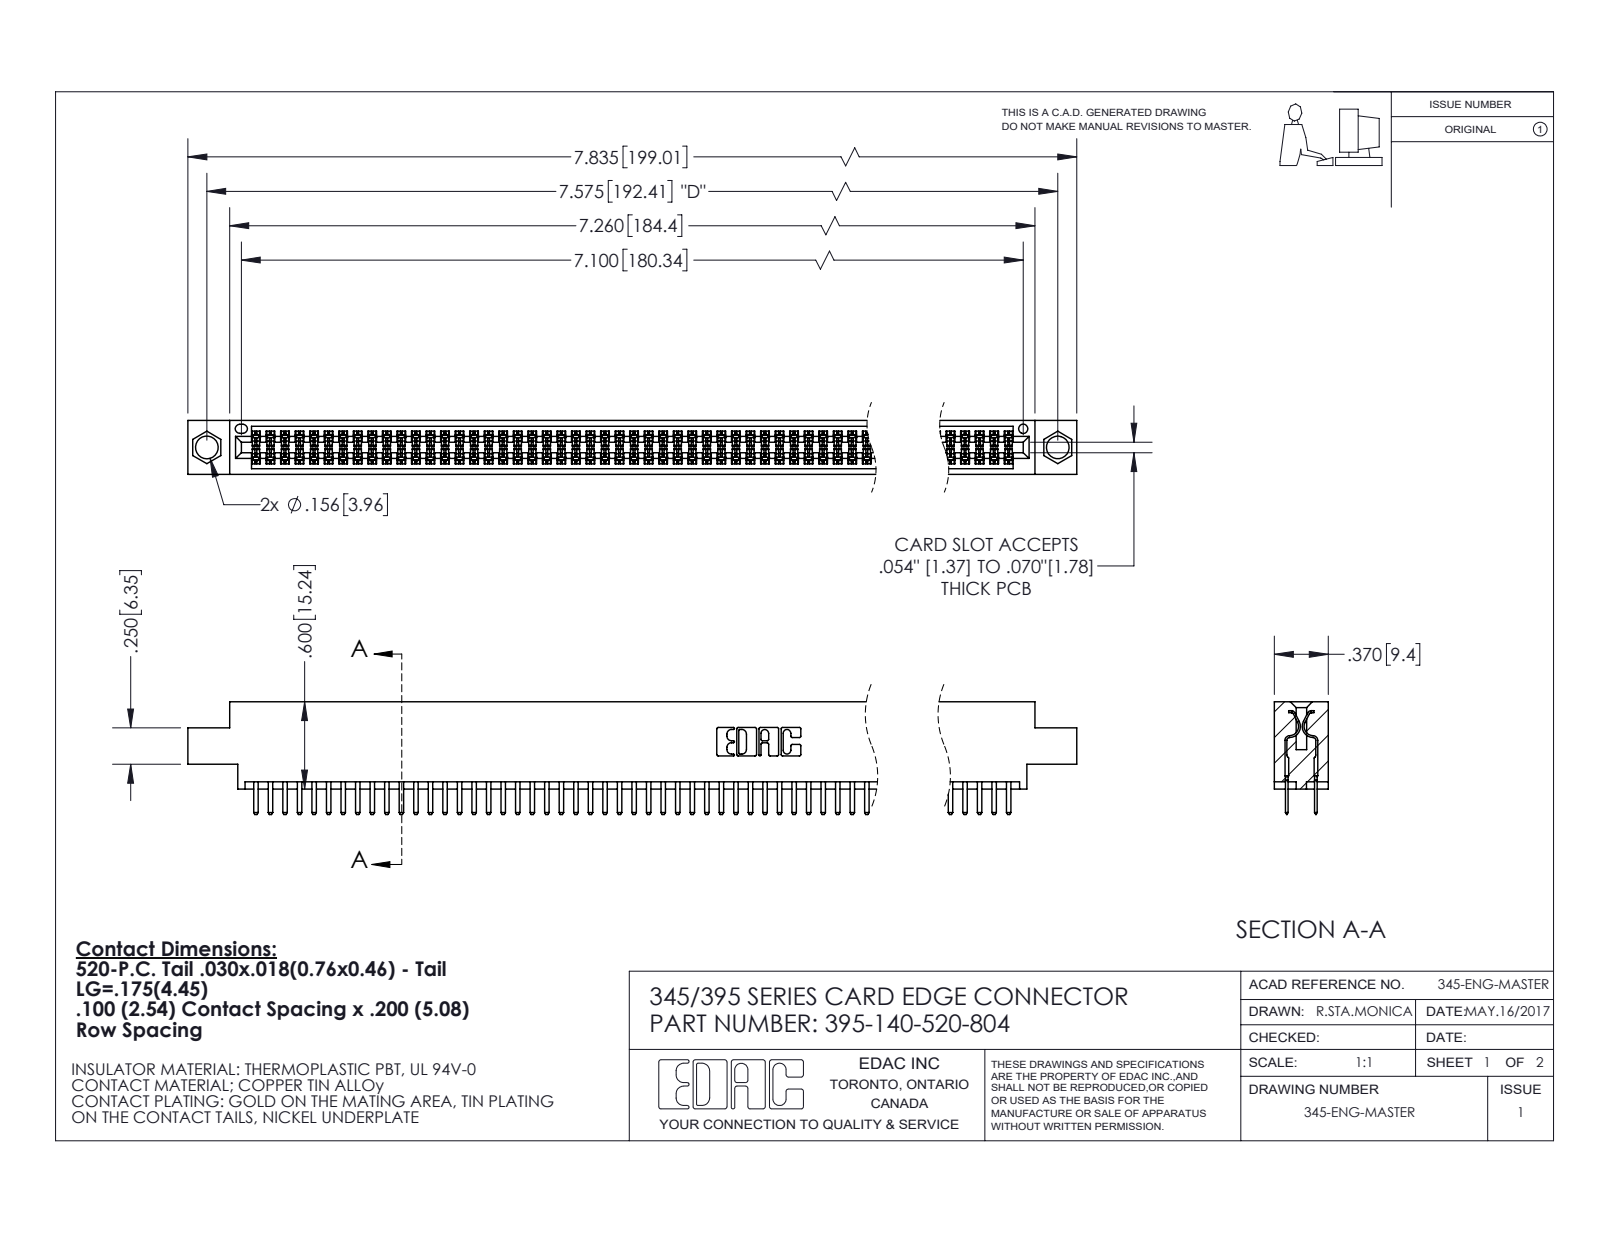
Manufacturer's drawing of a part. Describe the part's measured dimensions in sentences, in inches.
The part is named "345-292-001_345-293-120; 345 Part_0.170 Offset - 0.156 Dia-TI; 395-140-520-804". Its 3-D file was written by "SolidWorks 2020 (CONFIG_CONTROL_DESIGN)". It is 141 solids with 7704 faces: 4998 planar, 2706 cylindrical and 0 other. Overall it measures 7.835 by 0.775 by 0.37 inches. Its volume is 1.178 cubic inches and its surface area 44.87 square inches. Round holes: 2 of diameter 0.156, 1 of diameter 0.064. Partial cylindrical surfaces (rounded edges, fillets, slot ends): 210 of radius 0.006, 144 of radius 0.01, 22 of radius 0.01, 6 of radius 0.007, 6 of radius 0.031, 3 of radius 0.026, 2 of radius 0.014, 2 of radius 0.019. The main face-to-face distances are 0.072, 0.298, 0.2, 0.37, 0.098, 0.272, 0.025, 0.225, 0.022, 0.072. The hole center spacings are 0.27, 7.339, 7.575.
